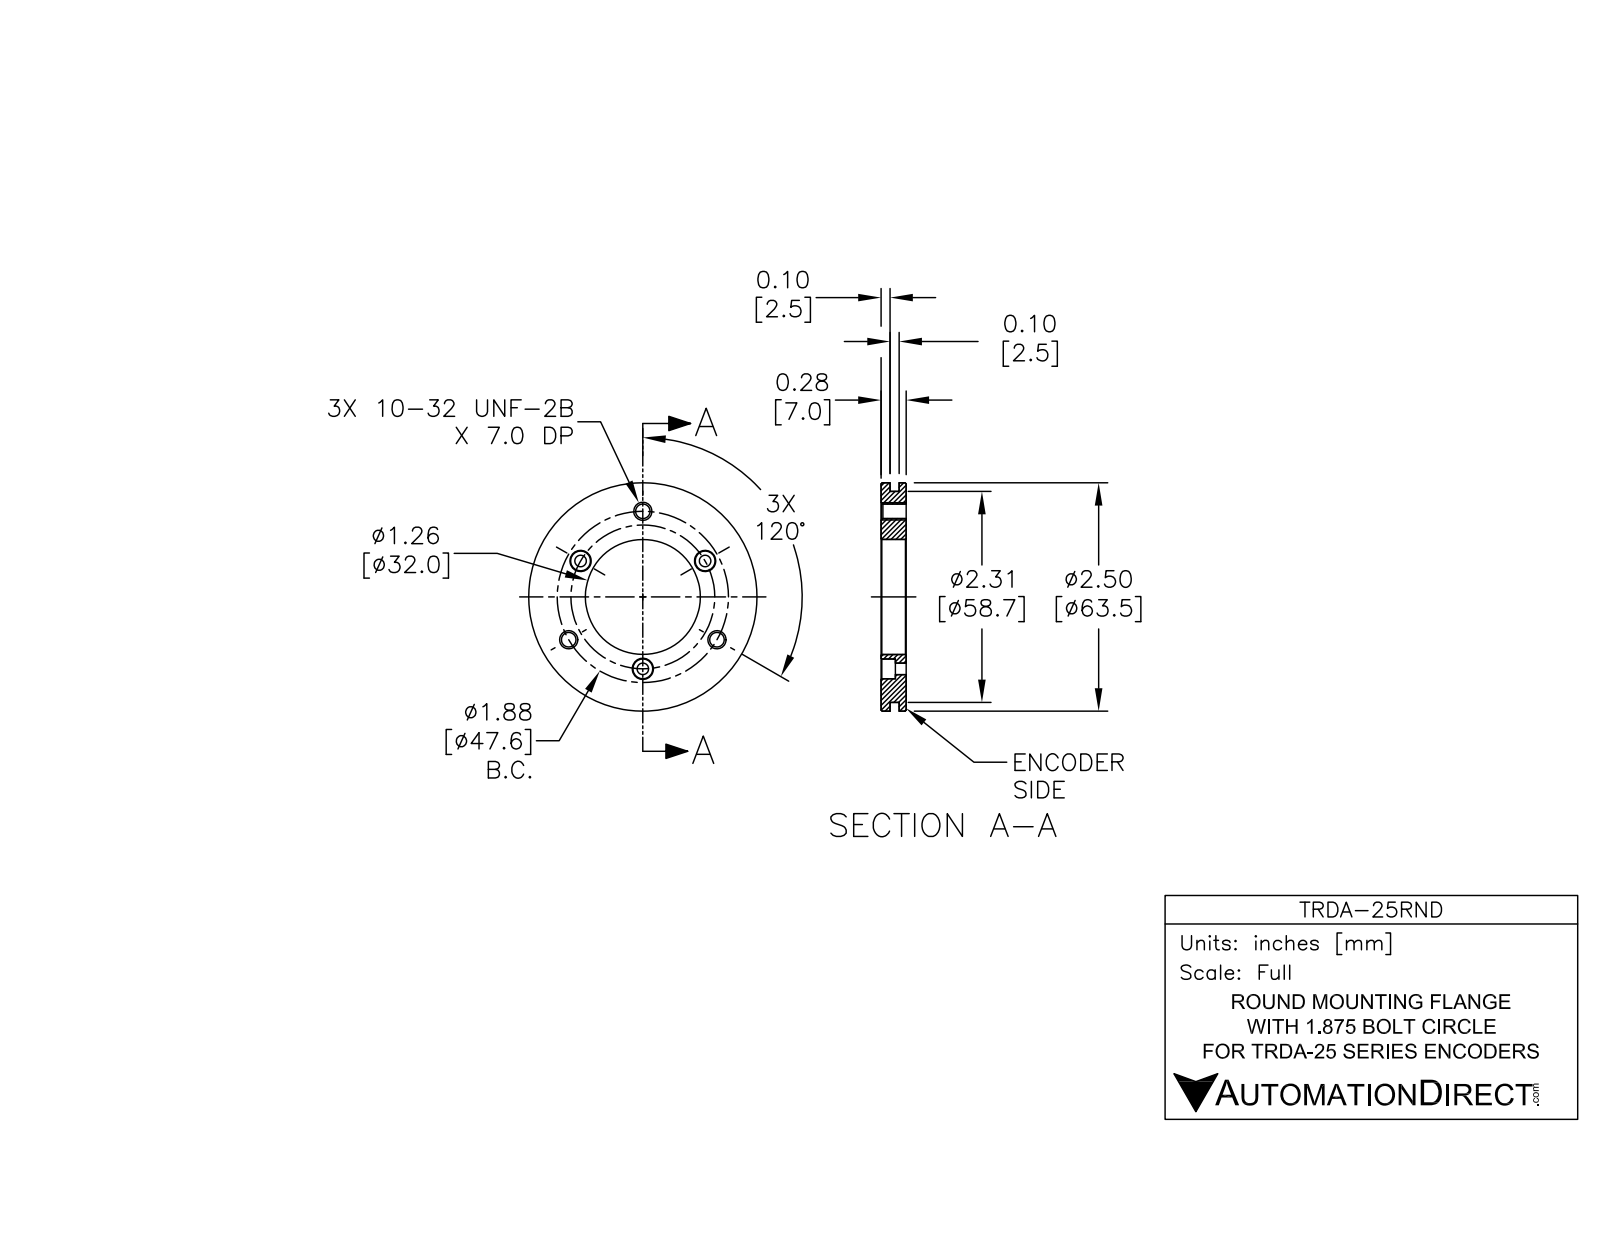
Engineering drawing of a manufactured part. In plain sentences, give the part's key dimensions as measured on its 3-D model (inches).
The part is named "TRDA-25RND". Its 3-D file was written by "SolidWorks 2017 (AUTOMOTIVE_DESIGN)". It is 4 solids with 65 faces: 13 planar, 32 cylindrical and 20 other. Overall it measures 2.5 by 2.5 by 0.276 inches. Its volume is 0.921 cubic inches and its surface area 13.12 square inches. Round holes: 3 of diameter 0.126, 3 of diameter 0.159, 3 of diameter 0.217, 1 of diameter 1.26. Round bosses or shafts: 3 of diameter 0.19, 1 of diameter 2.5, 1 of diameter 2.31. The main face-to-face distances are 0.276, 0.077, 0.177, 0.1, 0.198, 0.098, 0.271, 0.194, 0.094, 0.118. The hole center spacings are 0.872, 0.787, 1.364, 0.872, 0.937, 1.624, 1.725, 0.938.
